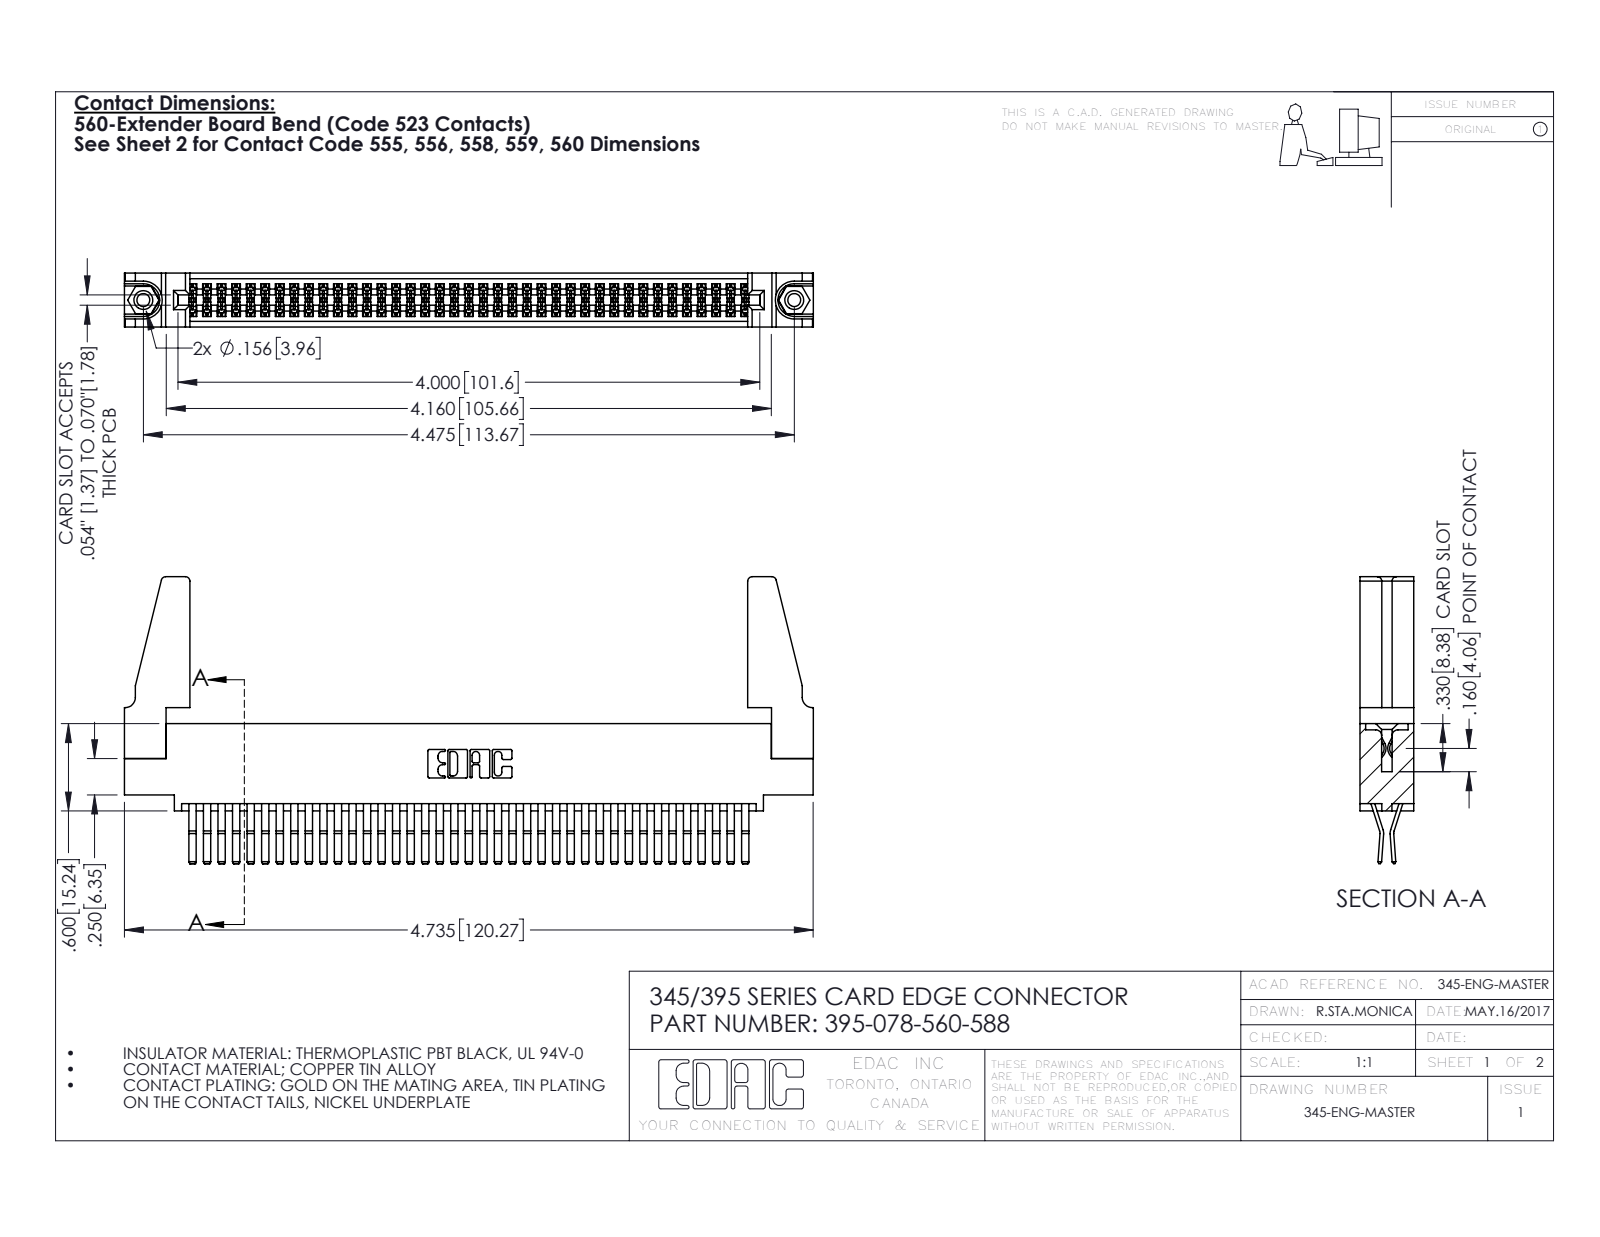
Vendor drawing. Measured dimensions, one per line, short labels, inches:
name: 345-250-001_345-250-001-102; 345-292-001_560 Tail; 395-078-560-588; 345 Part_0.110 Offset - 0.156 Dia-TH (+1 more)
written by: SolidWorks 2016 (CONFIG_CONTROL_DESIGN)
unit: in
bodies: 83 solids, 4310 faces (2730 planar, 1564 cylindrical, 16 other)
size: 4.736 × 1.972 × 0.37
volume: 0.937 in³; area: 34.64 in²
holes: 2× ⌀0.089, 2× ⌀0.125, 2× ⌀0.156, 1× ⌀0.064
bosses: 2× ⌀0.155
rounds: 117× R0.006, 22× R0.01, 8× R0.03, 6× R0.007, 6× R0.031, 3× R0.026, 2× R0.01, 2× R0.014
face distances: 0.072, 0.298, 0.025, 0.37, 0.2, 0.098, 0.272, 0.225, 0.175, 0.149
hole spacings: 0.27, 4.239, 4.475
